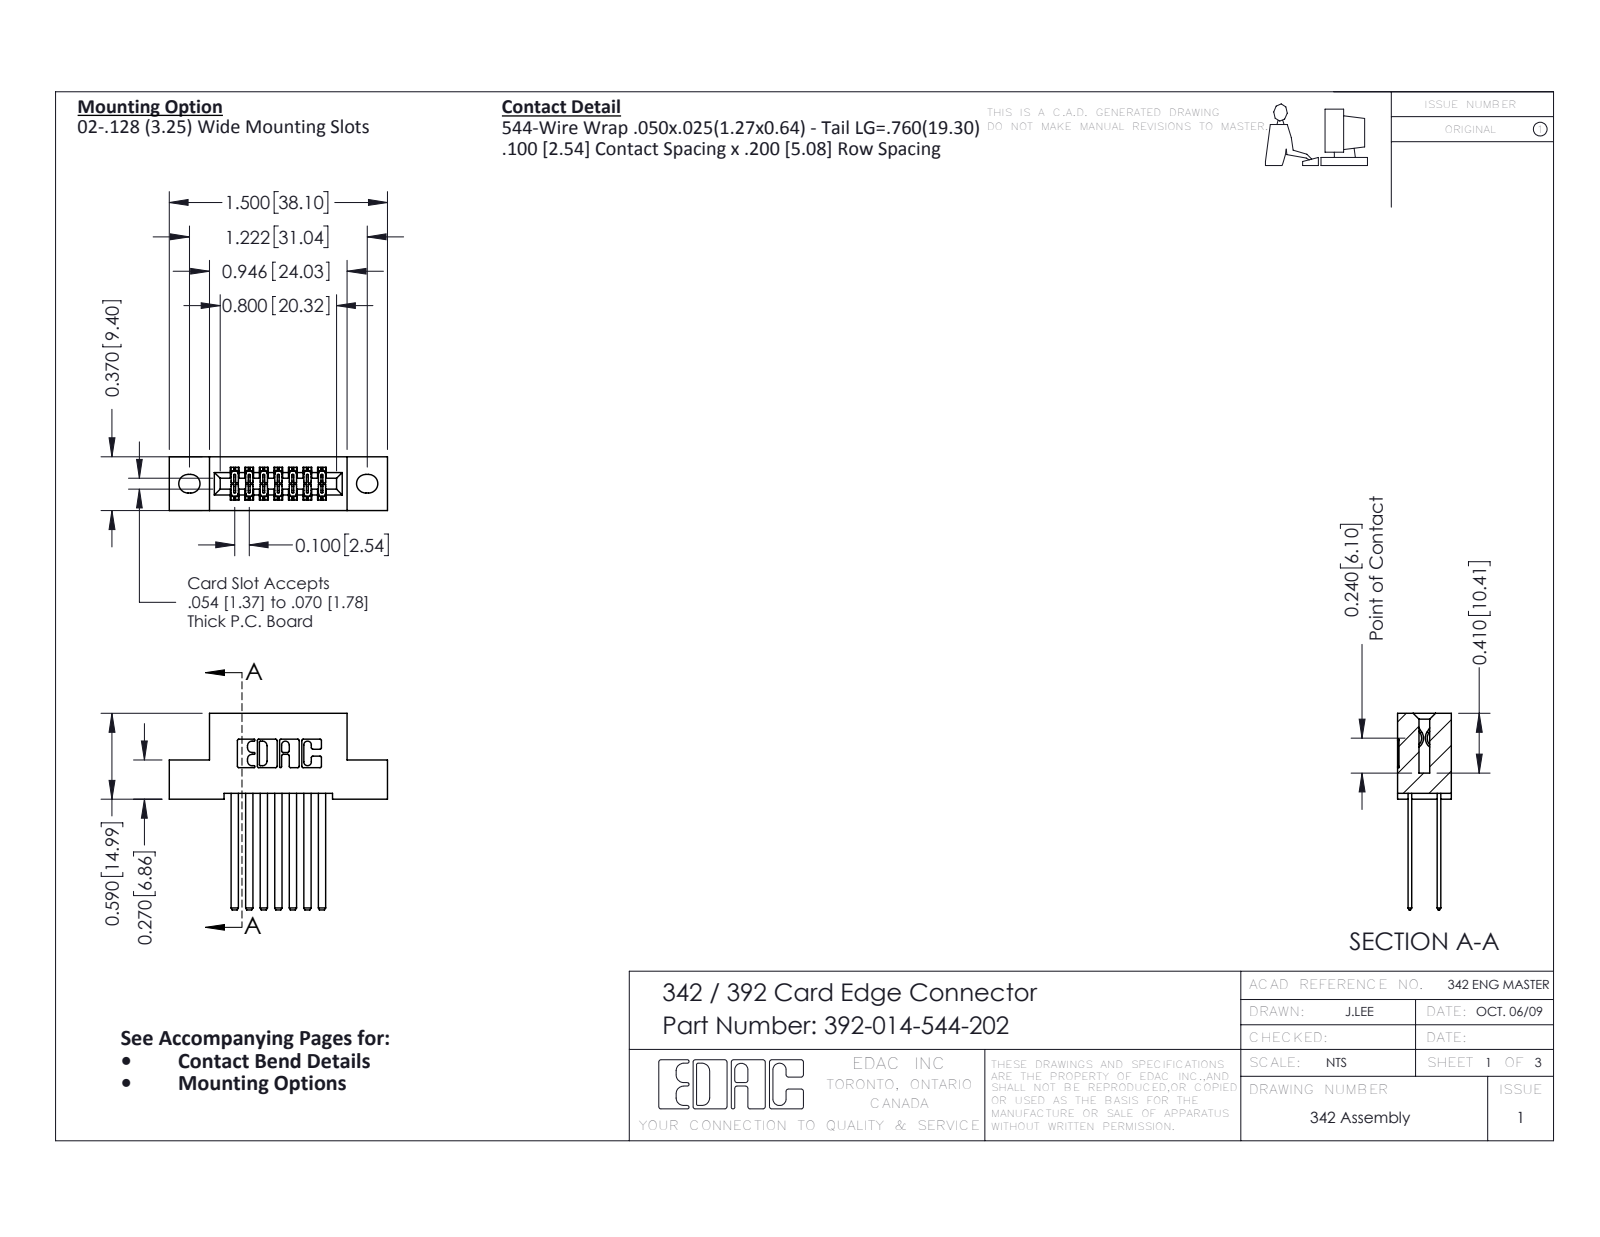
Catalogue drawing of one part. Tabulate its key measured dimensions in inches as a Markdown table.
| quantity | value |
| --- | --- |
| part name | 342 Part_.128 Slot; 345-292-001_345-293-144; 392-014-544-202 |
| STEP written by | SolidWorks 2016 (CONFIG_CONTROL_DESIGN) |
| units | inches |
| bodies | 15 solids, 758 faces (518 planar, 240 cylindrical, 0 other) |
| overall size | 1.5 × 1.35 × 0.37 |
| volume | 0.208 in³ |
| surface area | 7.715 in² |
| partial cylindrical surfaces (radius × count) | 0.01 × 22, 0.006 × 21, 0.007 × 6, 0.031 × 6, 0.064 × 4, 0.026 × 3, 0.014 × 2, 0.022 × 2 |
| main face-to-face distances | 0.2, 0.072, 0.298, 0.1, 0.098, 0.272, 0.025, 0.04, 0.37, 0.225 |
